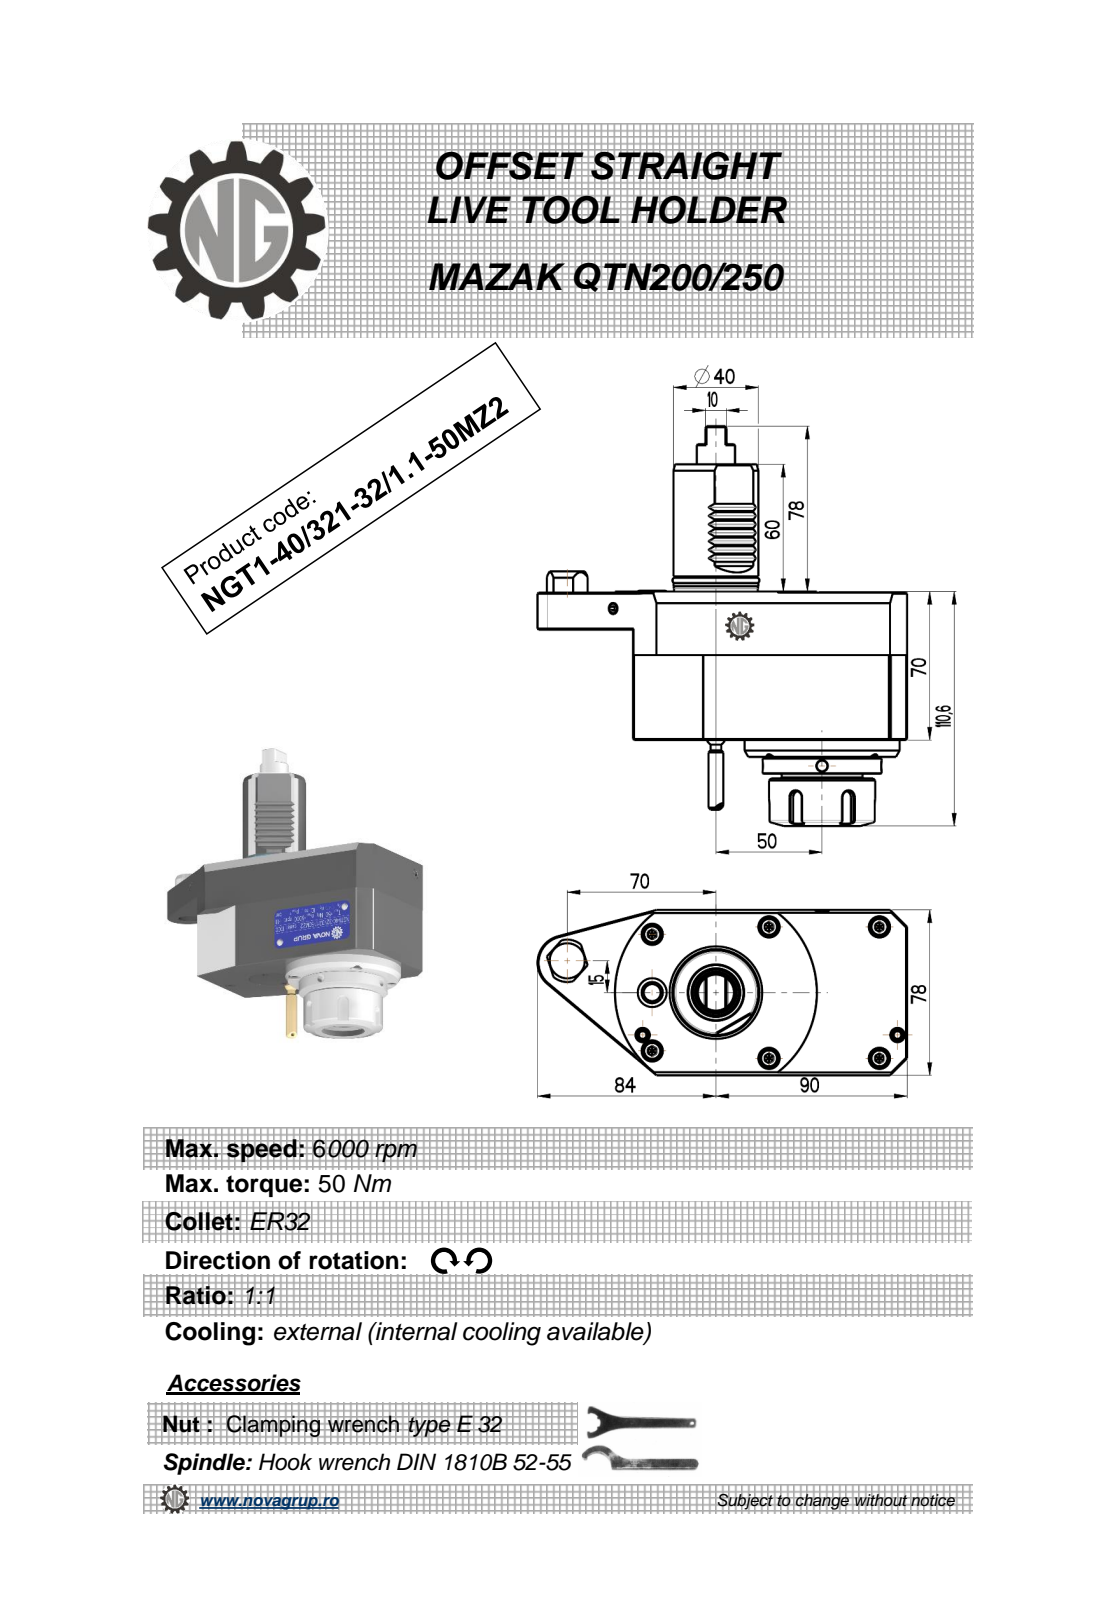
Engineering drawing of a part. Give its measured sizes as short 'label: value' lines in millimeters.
name: NGT1_40_321_32_1_1_50MZ2
written by: PRO/ENGINEER BY PARAMETRIC TECHNOLOGY CORPORATION, 2010280 (CONFIG_CONTROL_DESIGN)
unit: mm
bodies: 1 solid, 264 faces (111 planar, 67 cylindrical, 86 other)
size: 188.6 × 174 × 78
volume: 891 013 mm³; area: 73 983 mm²
holes: 2× ⌀5, 1× ⌀2.5, 1× ⌀3, 1× ⌀8, 1× ⌀27
bosses: 1× ⌀73, 1× ⌀56, 1× ⌀50, 1× ⌀42, 1× ⌀41, 1× ⌀40, 1× ⌀39.4, 1× ⌀36.2
rounds: 7× R0.3, 6× R0.16, 5× R3, 2× R0.8, 1× R10, 1× R12.97
face distances: 78, 70, 8, 129, 60, 18, 52, 88.1, 86, 68
hole spacings: 36.91, 54.43, 80
